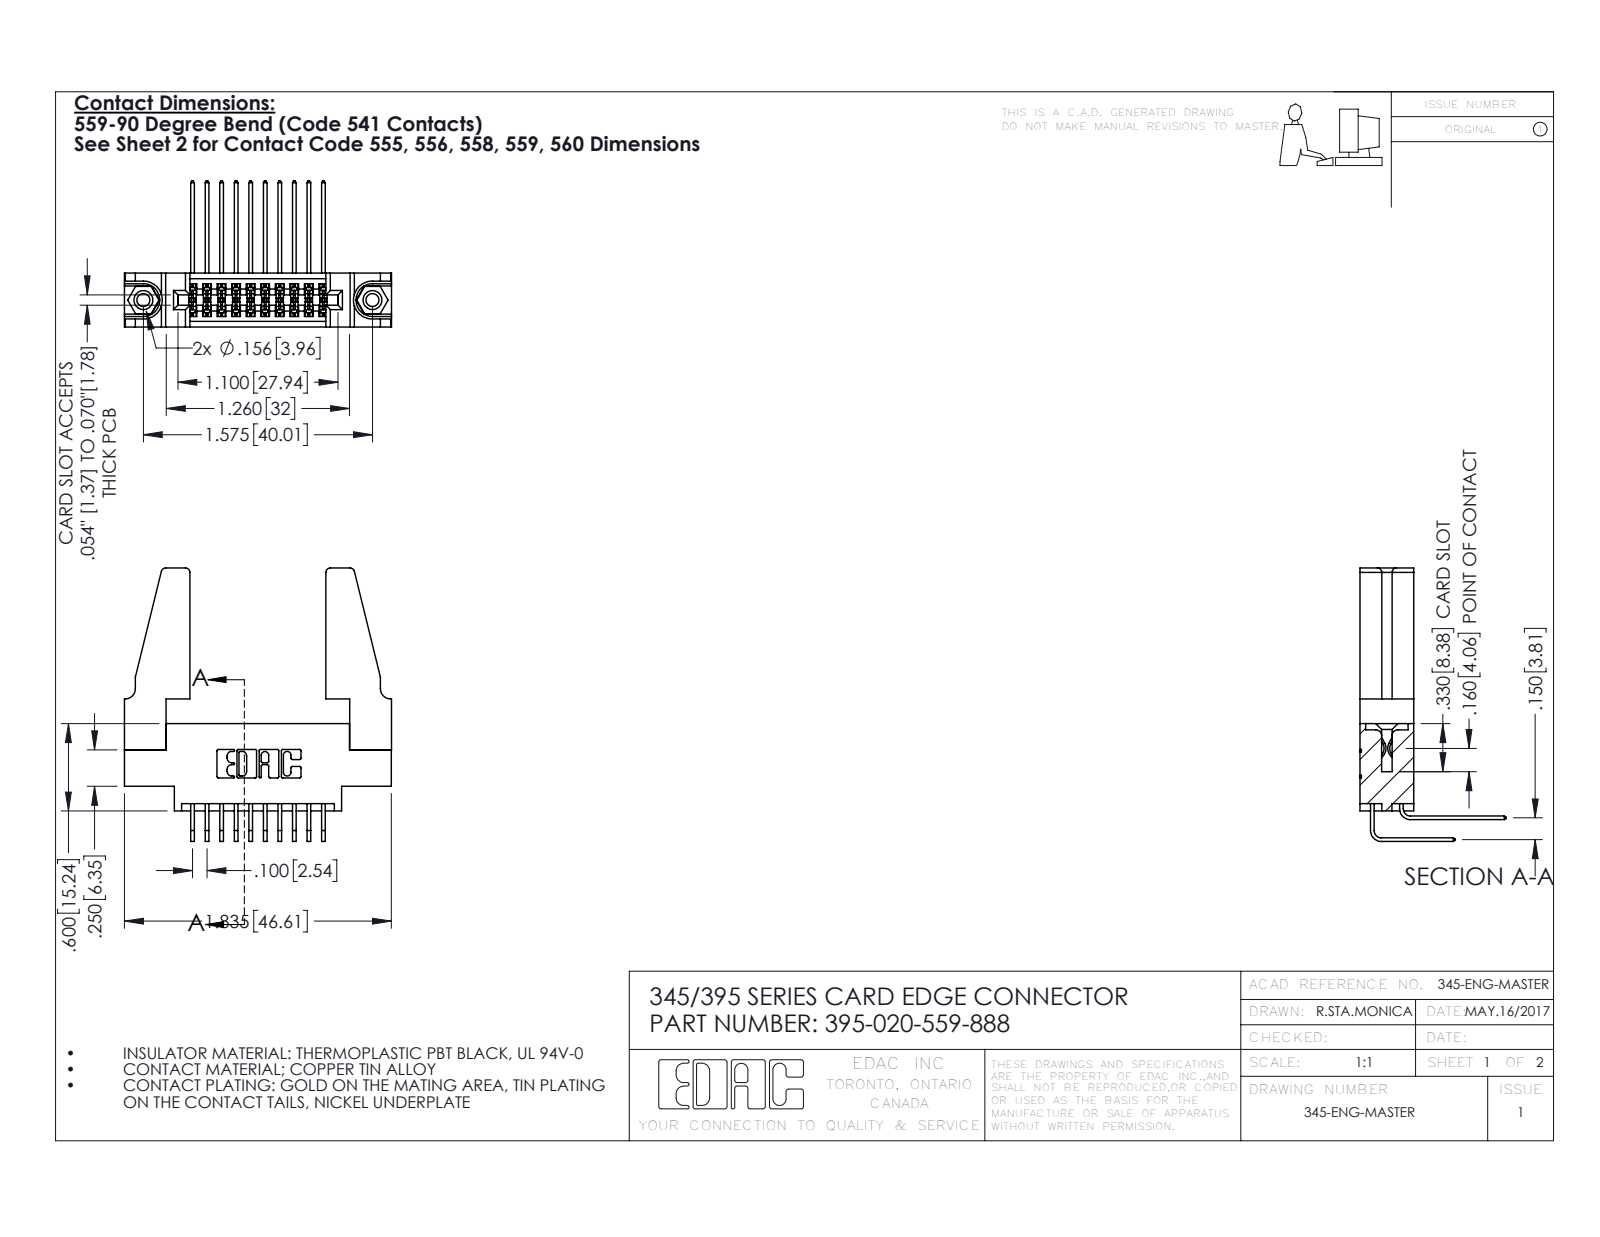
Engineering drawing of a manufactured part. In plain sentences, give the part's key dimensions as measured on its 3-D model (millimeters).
The part is named "395-020-559-888; 345-292-001_558 559 Tail - 1; 345-292-001_559 Tail - 2; 345-250-001_345-250-001-102 (+2 more)". Its 3-D file was written by "SolidWorks 2016 (CONFIG_CONTROL_DESIGN)". It is 25 solids with 1294 faces: 856 planar, 422 cylindrical and 16 other. Overall it measures 47.7 by 46.6 by 25.5 millimeters. Its volume is 7 490 cubic millimeters and its surface area 9 452 square millimeters. Round holes: 2 of diameter 2.3, 2 of diameter 3.2, 2 of diameter 4, 1 of diameter 1.6. Round bosses or shafts: 2 of diameter 3.9. Partial cylindrical surfaces (rounded edges, fillets, slot ends): 31 of radius 0.2, 22 of radius 0.3, 8 of radius 0.8, 6 of radius 0.2, 6 of radius 0.8, 3 of radius 0.7, 2 of radius 0.4, 2 of radius 0.5. The main face-to-face distances are 9.4, 1.8, 7.6, 5.1, 2.5, 6.9, 0.6, 3.8, 5.7, 4.4. The hole center spacings are 6.9, 34.1, 40.
